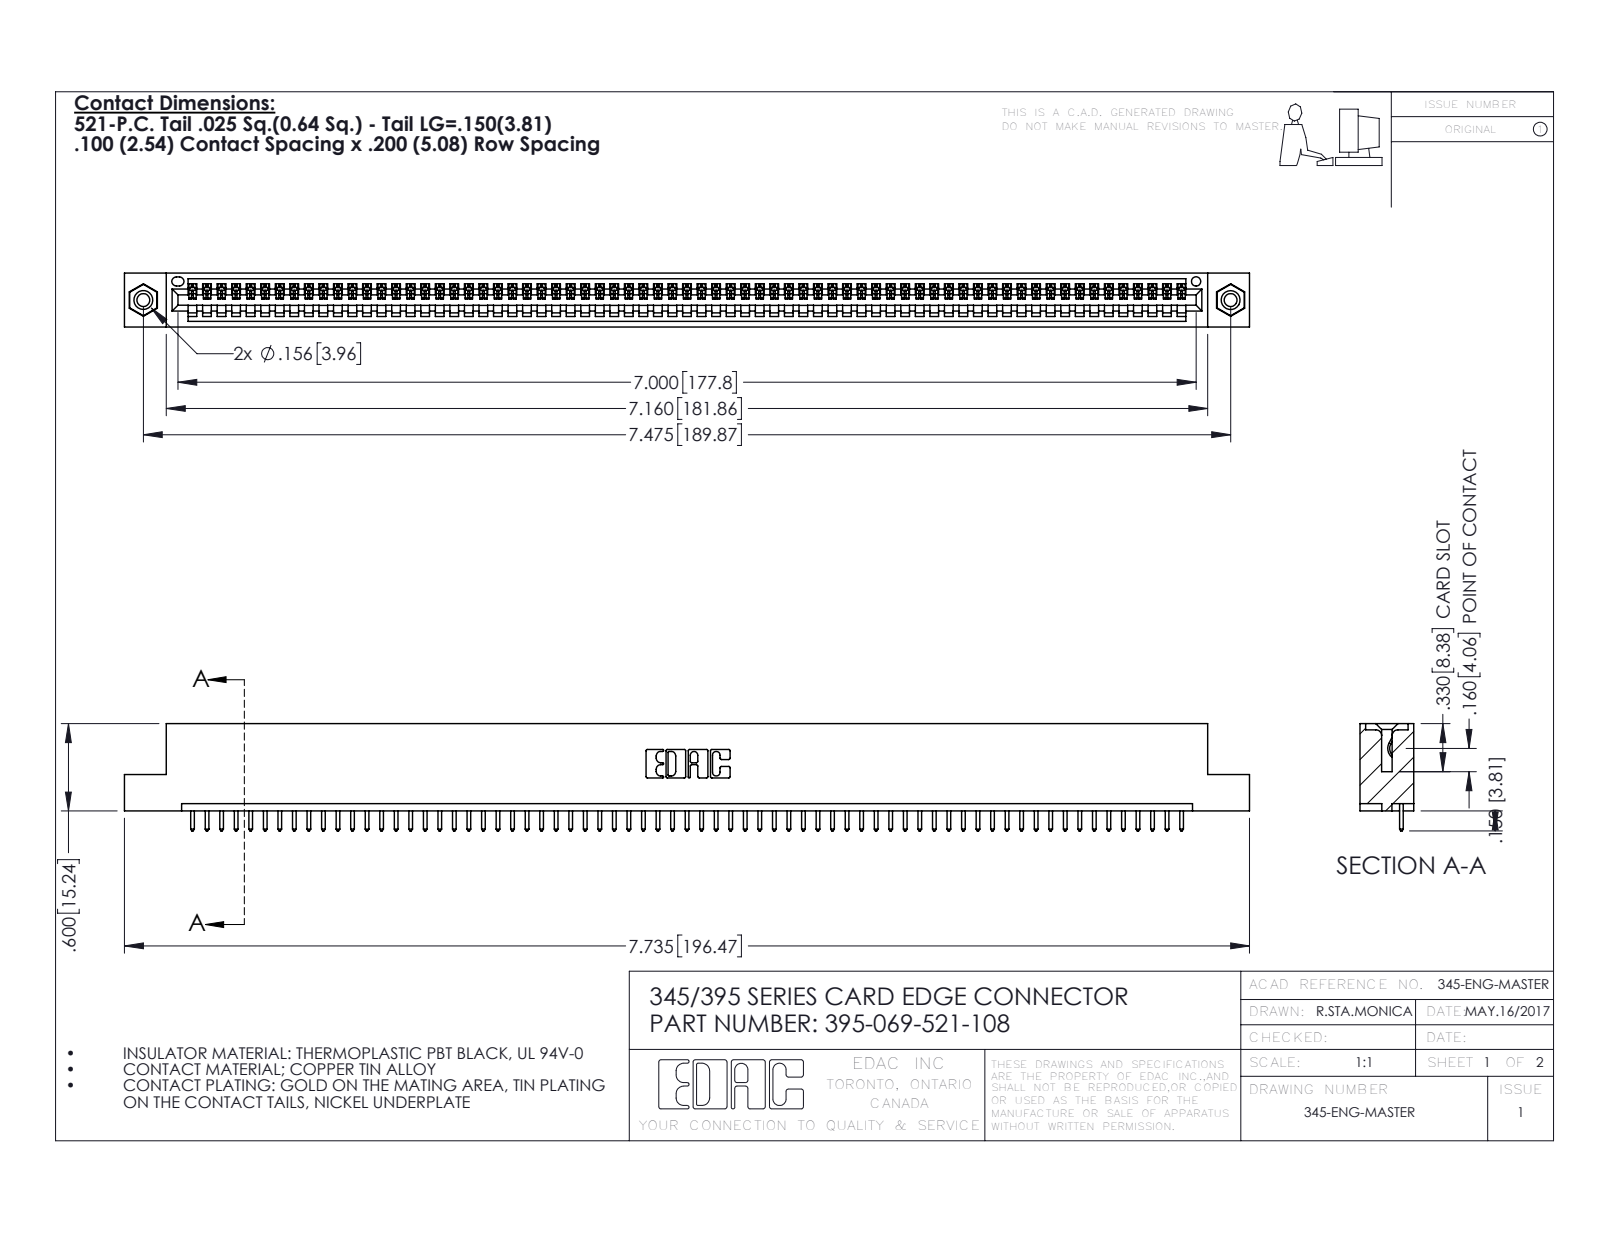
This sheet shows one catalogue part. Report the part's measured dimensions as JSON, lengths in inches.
{"part_name": "345 Part_Flush Mounting Lugs - 0.156 Dia-TI; 345-250-001_345-250-003-102; 395-069-521-108; 345-292-001_345-293-121", "step_written_by": "SolidWorks 2016 (CONFIG_CONTROL_DESIGN)", "units": "inches", "bodies": {"solids": 72, "faces": 4188, "planar": 2872, "cylindrical": 1300, "other": 16}, "overall_size": [7.735, 0.737, 0.37], "volume_in3": 1.14, "surface_area_in2": 37.88, "round_holes": [[0.089, 2], [0.125, 2], [0.156, 2], [0.064, 1]], "round_bosses_or_shafts": [[0.155, 2]], "partial_cylinders_radius": [[0.006, 138], [0.01, 138], [0.01, 22], [0.007, 6], [0.031, 6], [0.026, 3], [0.031, 2], [0.04, 2]], "face_to_face_distances": [0.072, 0.298, 0.37, 0.2, 0.098, 0.272, 0.025, 0.225, 0.149, 0.072], "hole_center_spacings": [0.27, 7.239, 7.475]}
